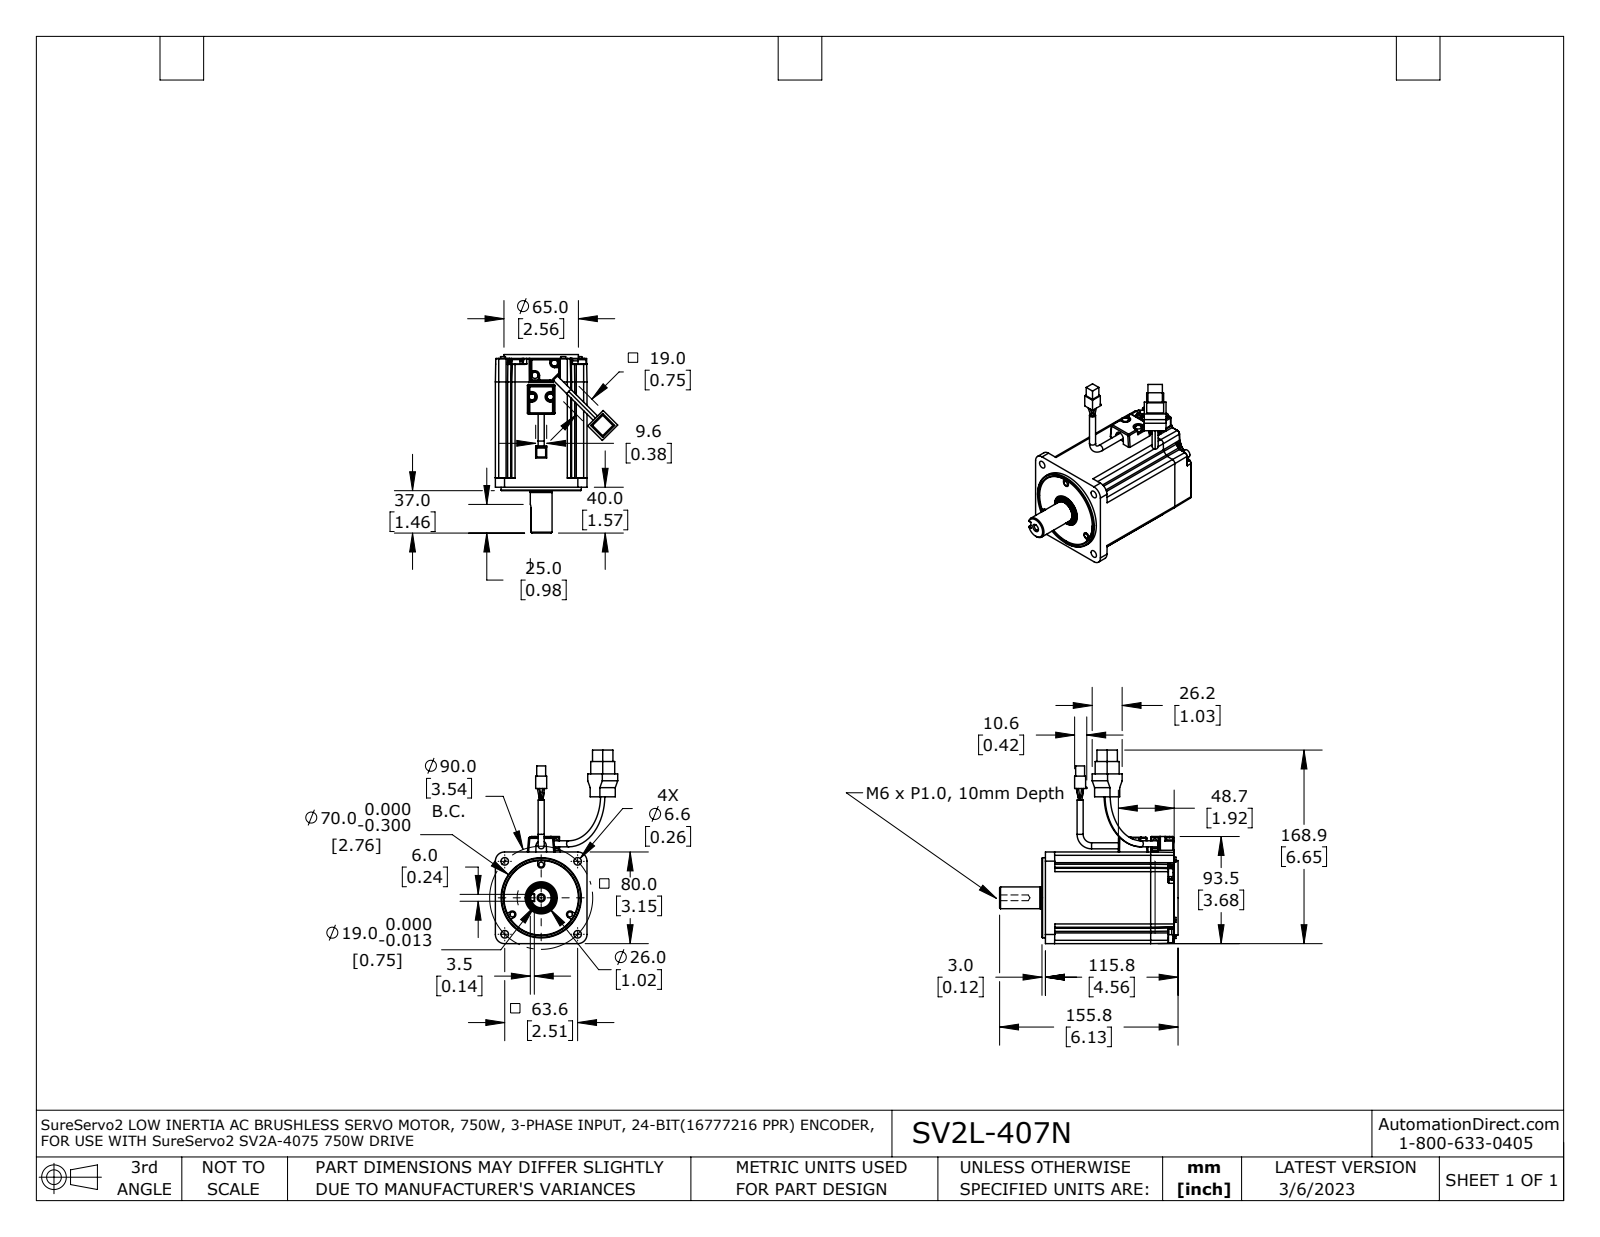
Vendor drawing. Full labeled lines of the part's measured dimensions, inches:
Part name (STEP PRODUCT): SV2L-x07N
STEP written by: SolidWorks 2021 (AUTOMOTIVE_DESIGN)
Units: inches
Bodies: 1 solid, 725 faces (223 planar, 294 cylindrical, 208 other)
Overall size (bounding box): 6.651 × 6.134 × 4.205
Volume: 42.24 in³ · Surface area: 97.58 in²
Round holes (diameter × count): ⌀0.26 ×4, ⌀0.197 ×1, ⌀0.236 ×1, ⌀1.024 ×1, ⌀1.102 ×1, ⌀2.559 ×1
Round bosses / shafts (diameter × count): ⌀0.169 ×7, ⌀0.276 ×4, ⌀0.217 ×4, ⌀0.209 ×4, ⌀0.059 ×4, ⌀0.228 ×2, ⌀2.756 ×1, ⌀0.945 ×1
Partial cylindrical surfaces — rounded edges, fillets, slot ends (radius × count): R0.039 ×46, R0.012 ×24, R0.118 ×22, R0.008 ×20, R0.079 ×16, R0.033 ×8, R0.072 ×8, R0.085 ×8
Main face-to-face distances: 3.15, 4.657, 4.559, 0.098, 0.138, 4.421, 4.52, 2.109, 0.118, 3.109
Hole centre spacings: 1.772, 2.506, 3.543
